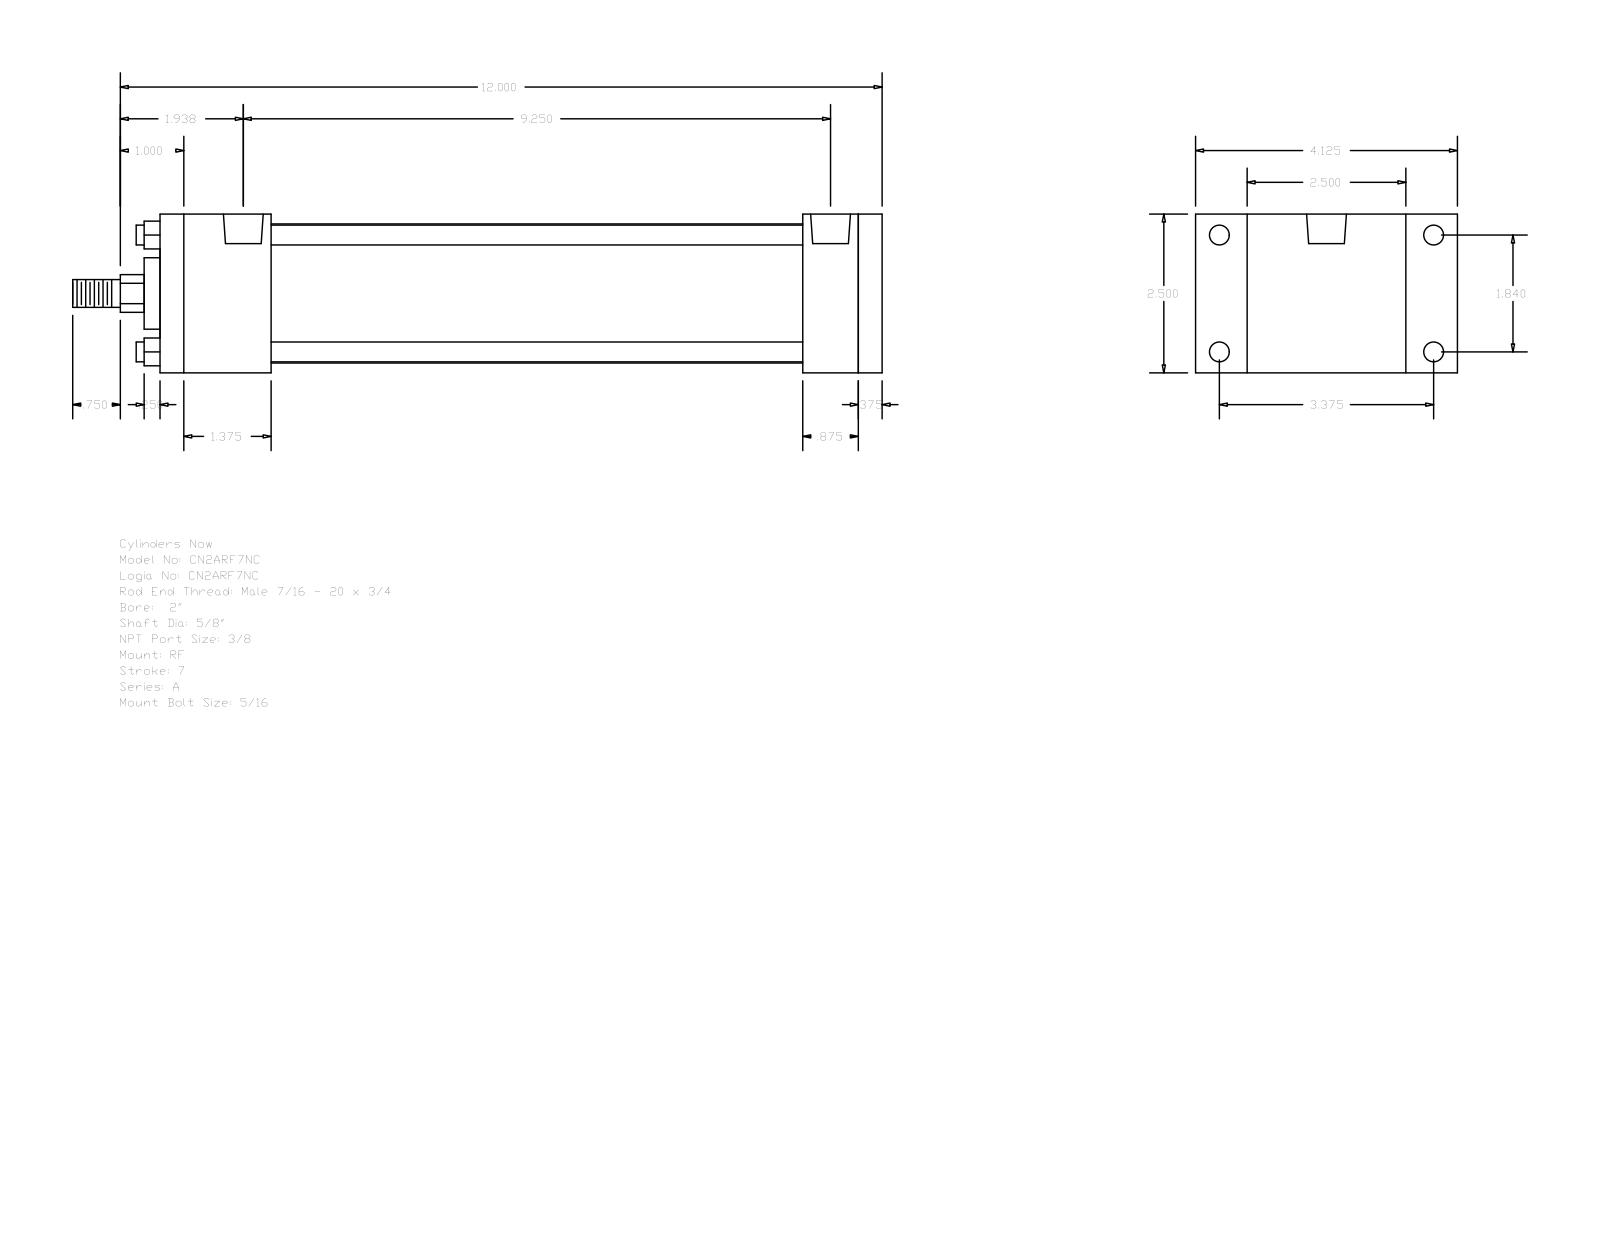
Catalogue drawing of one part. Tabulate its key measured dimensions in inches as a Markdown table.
| quantity | value |
| --- | --- |
| part name | A_RF__0200_0.625 |
| STEP written by | GSSL Pune (CONFIG_CONTROL_DESIGN) |
| units | inches |
| bodies | 0 solids, 92 faces (64 planar, 28 cylindrical, 0 other) |
| overall size | 12.75 × 4.125 × 2.5 |
| round holes (diameter × count) | 0.219 × 4, 0.313 × 4, 0.627 × 2 |
| round bosses / shafts (diameter × count) | 0.313 × 4, 2.19 × 1, 1.125 × 1, 0.625 × 1, 0.437 × 1 |
| partial cylindrical surfaces (radius × count) | 0.297 × 1 |
| main face-to-face distances | 2.5, 11.375, 0.375, 11, 1.75, 9.25, 9.625, 10.125, 8.375, 0.875 |
| hole center spacings | 1.84, 3.375, 3.844, 8.937, 0.156, 0.157, 9.093, 9.094 |
